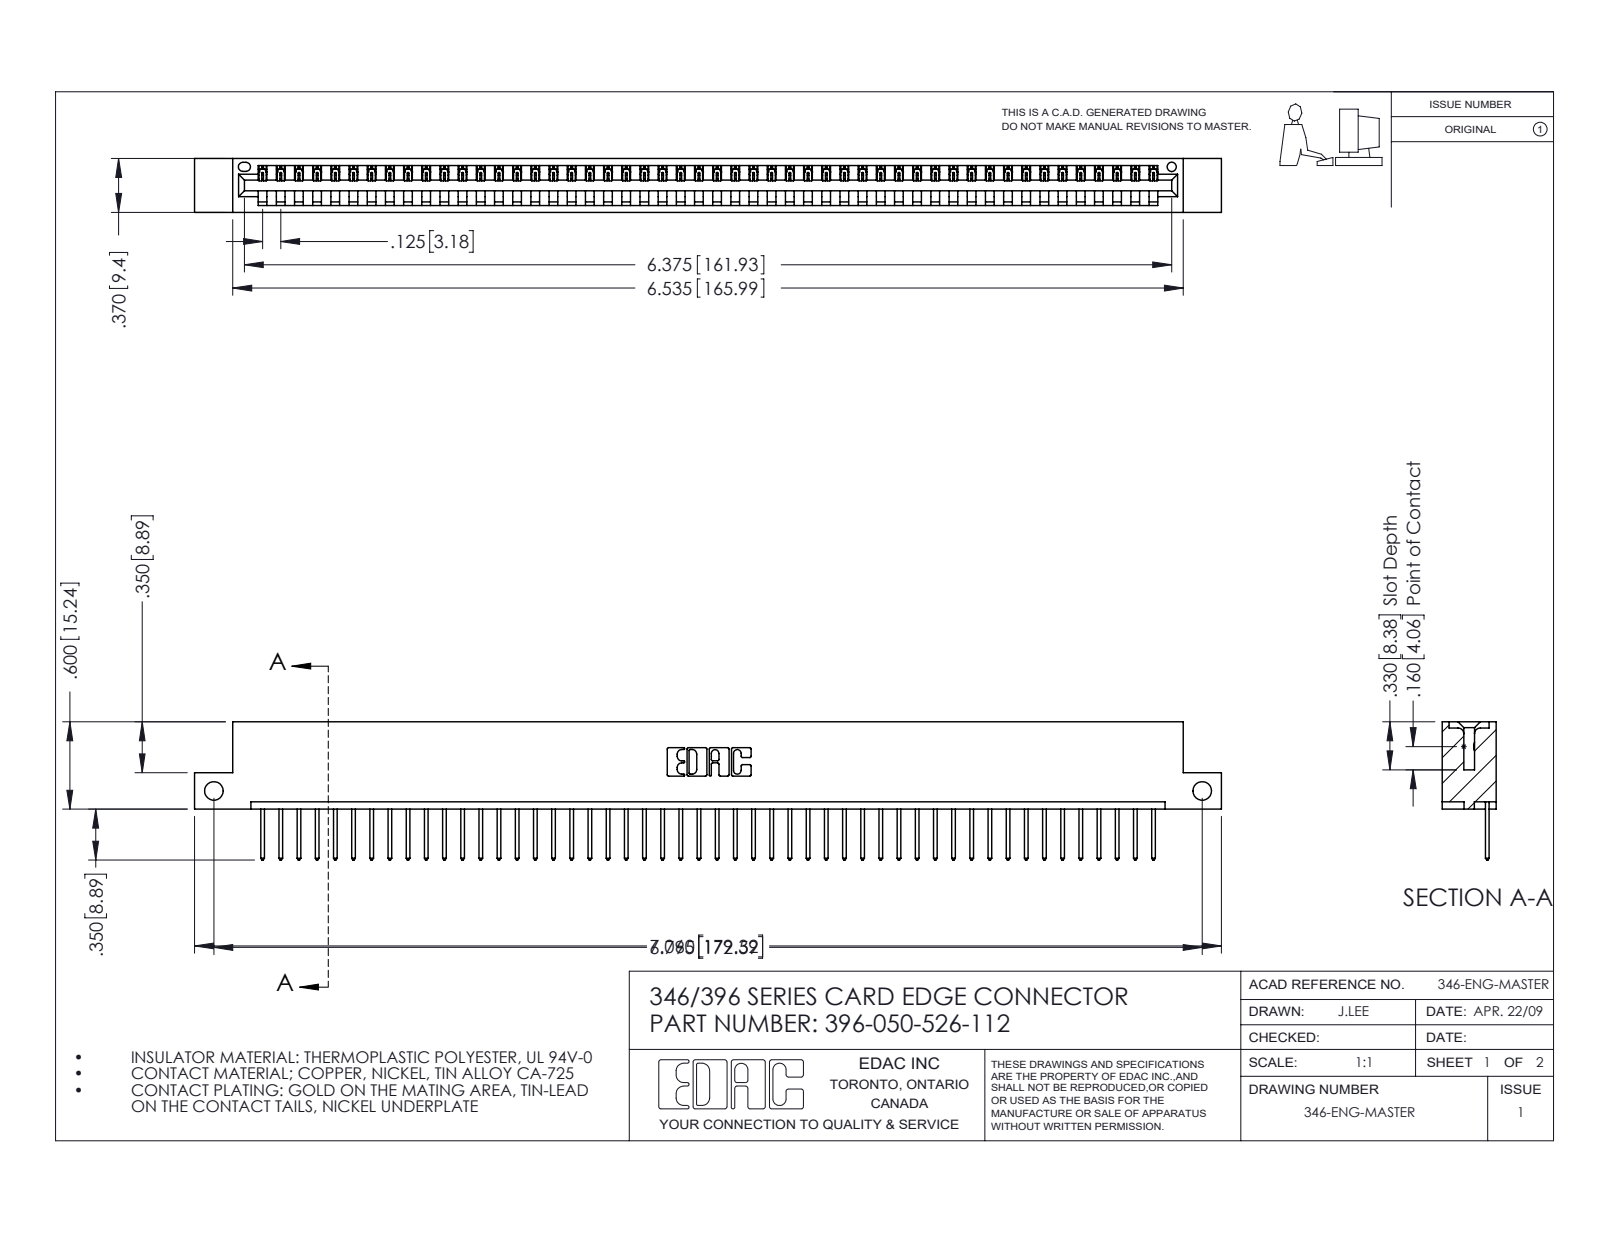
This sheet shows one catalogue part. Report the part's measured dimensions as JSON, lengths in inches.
{"part_name": "345-292-001_345-293-126; 396-050-526-112; 346 Part_Flush Mounting Lugs - Side Mount", "step_written_by": "SolidWorks 2016 (CONFIG_CONTROL_DESIGN)", "units": "inches", "bodies": {"solids": 51, "faces": 3022, "planar": 2076, "cylindrical": 946, "other": 0}, "overall_size": [7.06, 0.95, 0.37], "volume_in3": 1.043, "surface_area_in2": 32.95, "round_holes": [[0.128, 2], [0.064, 1]], "partial_cylinders_radius": [[0.006, 100], [0.01, 100], [0.01, 22], [0.007, 6], [0.031, 6], [0.026, 3], [0.031, 2], [0.04, 2]], "face_to_face_distances": [0.048, 0.322, 0.37, 0.25, 0.072, 0.298, 0.025, 0.148, 0.222, 0.1], "hole_center_spacings": [6.795]}
